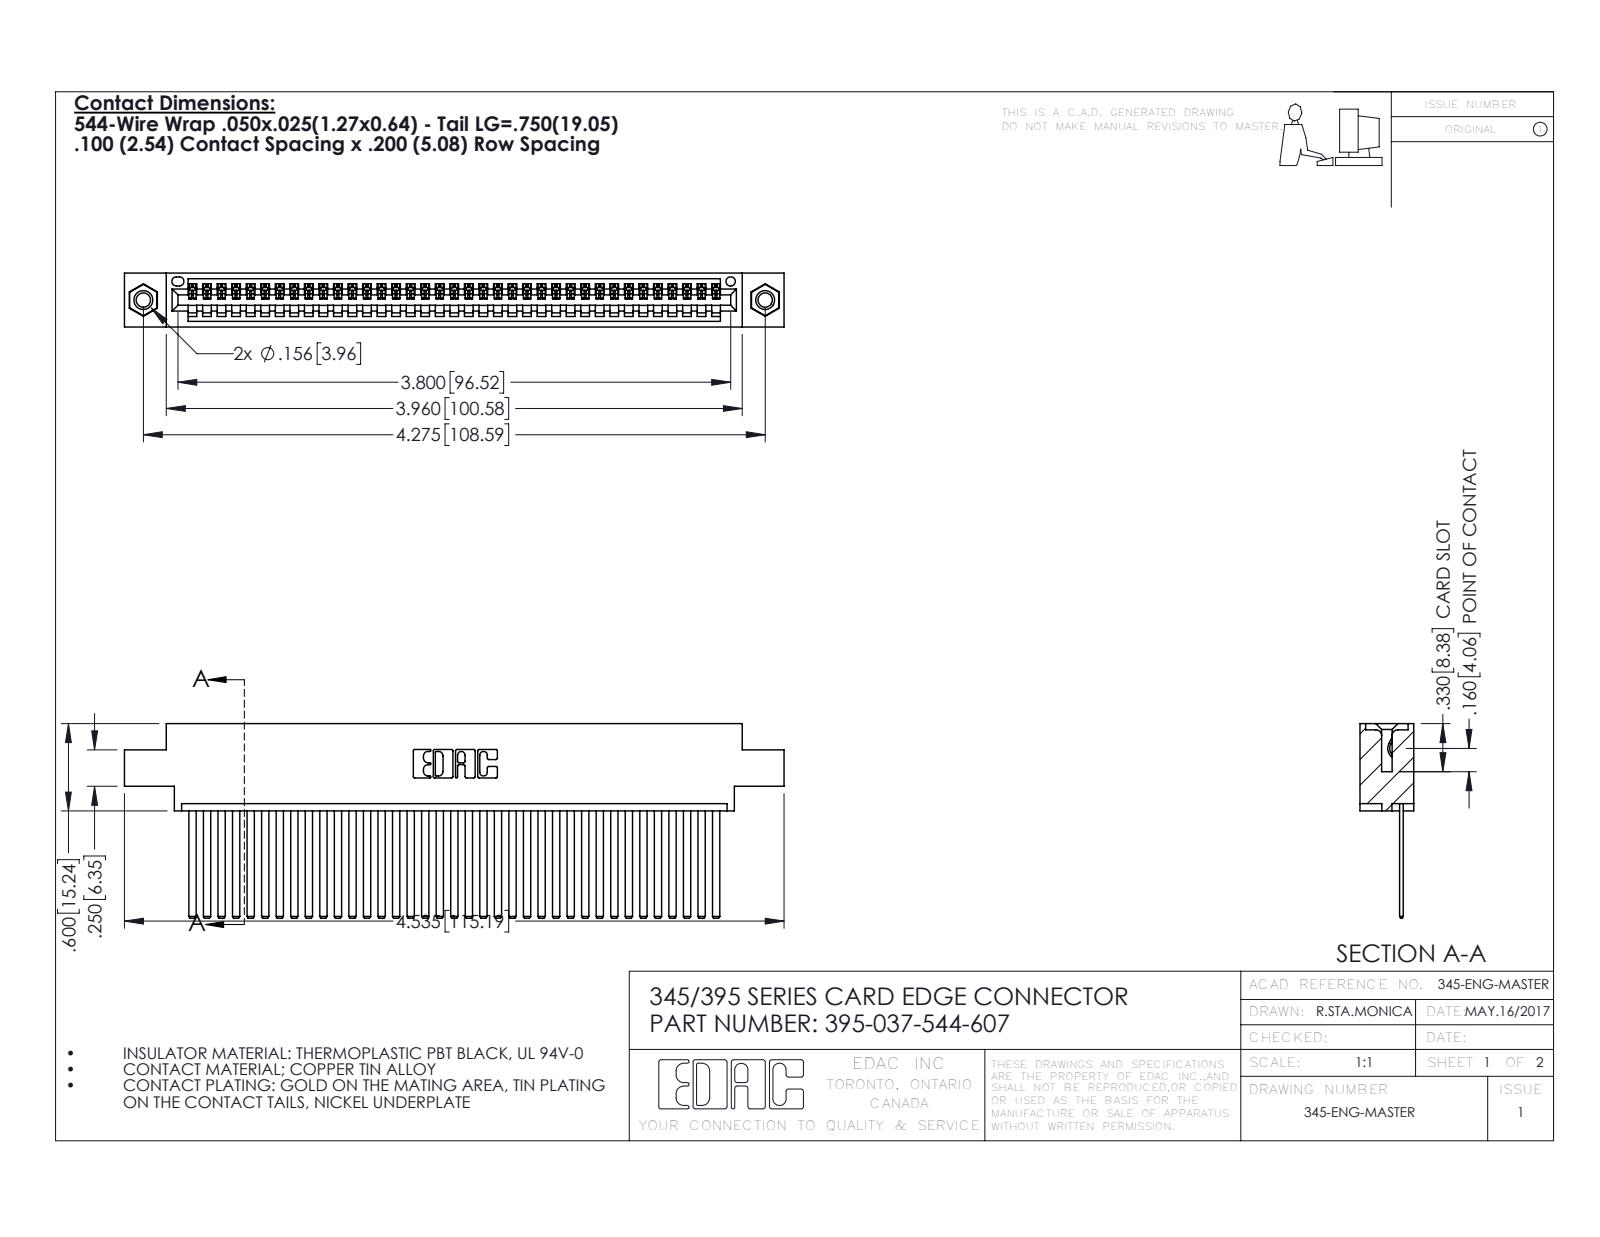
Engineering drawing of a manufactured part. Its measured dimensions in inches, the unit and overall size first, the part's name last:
Units: inches
Overall size (bounding box): 4.535 × 1.337 × 0.37
Round holes (diameter × count): ⌀0.098 ×2, ⌀0.125 ×2, ⌀0.156 ×2, ⌀0.064 ×1
Round bosses / shafts (diameter × count): ⌀0.155 ×2
Partial cylindrical surfaces — rounded edges, fillets, slot ends (radius × count): R0.006 ×74, R0.01 ×22, R0.007 ×6, R0.031 ×6, R0.026 ×3, R0.031 ×2, R0.04 ×2, R0.014 ×1
Main face-to-face distances: 0.072, 0.298, 0.025, 0.098, 0.272, 0.37, 0.2, 0.225, 0.175, 0.149
Hole centre spacings: 0.27, 4.039, 4.275
Volume: 0.684 in³ · Surface area: 25.21 in²
Bodies: 40 solids, 2114 faces (1448 planar, 650 cylindrical, 16 other)
Part name (STEP PRODUCT): 345-250-001_345-250-005-103; 345-292-001_345-293-144; 345 Part_0.170 Offset - 0.156 Dia-TI; 395-037-544-607
STEP written by: SolidWorks 2016 (CONFIG_CONTROL_DESIGN)
